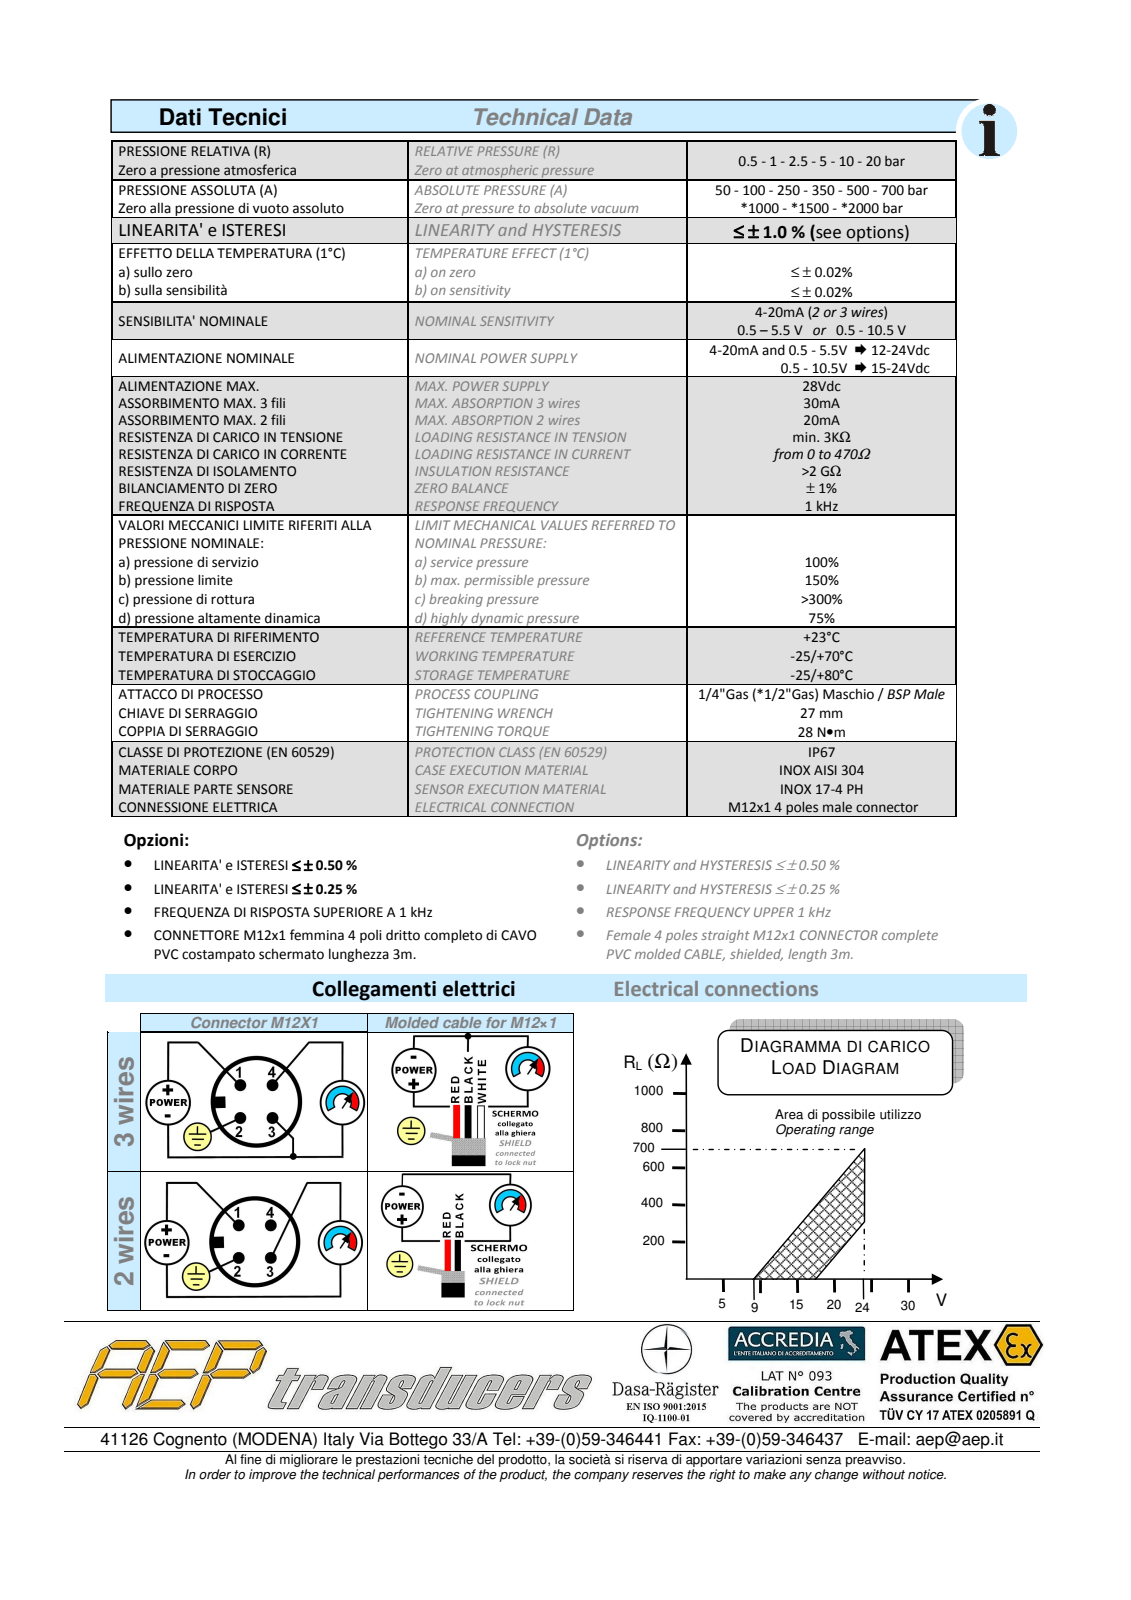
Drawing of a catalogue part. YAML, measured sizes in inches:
part_name: "TP38; 4 poles contact holder; Head; Enclosure"
step_written_by: "Spatial InterOp 3D (automotive_design)"
units: inches
bodies: {solids: 7, faces: 150, planar: 37, cylindrical: 51, other: 62}
overall_size: [2.442, 1.201, 1.063]
volume: 1.299
surface_area: 17.09
round_holes:
  - {diameter: 0.053, count: 4}
  - {diameter: 0.283, count: 1}
  - {diameter: 0.291, count: 1}
  - {diameter: 0.331, count: 1}
  - {diameter: 0.335, count: 1}
  - {diameter: 0.451, count: 1}
round_bosses_or_shafts:
  - {diameter: 1.063, count: 1}
  - {diameter: 1.02, count: 1}
  - {diameter: 0.906, count: 1}
  - {diameter: 0.518, count: 1}
  - {diameter: 0.445, count: 1}
  - {diameter: 0.409, count: 1}
  - {diameter: 0.37, count: 1}
  - {diameter: 0.307, count: 1}
partial_cylinders:
  - {radius: 0.6, count: 1}
face_to_face_distances: [0.776, 1.063, 0.079, 0.697, 0.551, 1.469, 1.391, 0.694, 1.568, 1.489]
hole_center_spacings: [0.106, 0.15, 0.151, 0.106, 0.213, 0.213]
